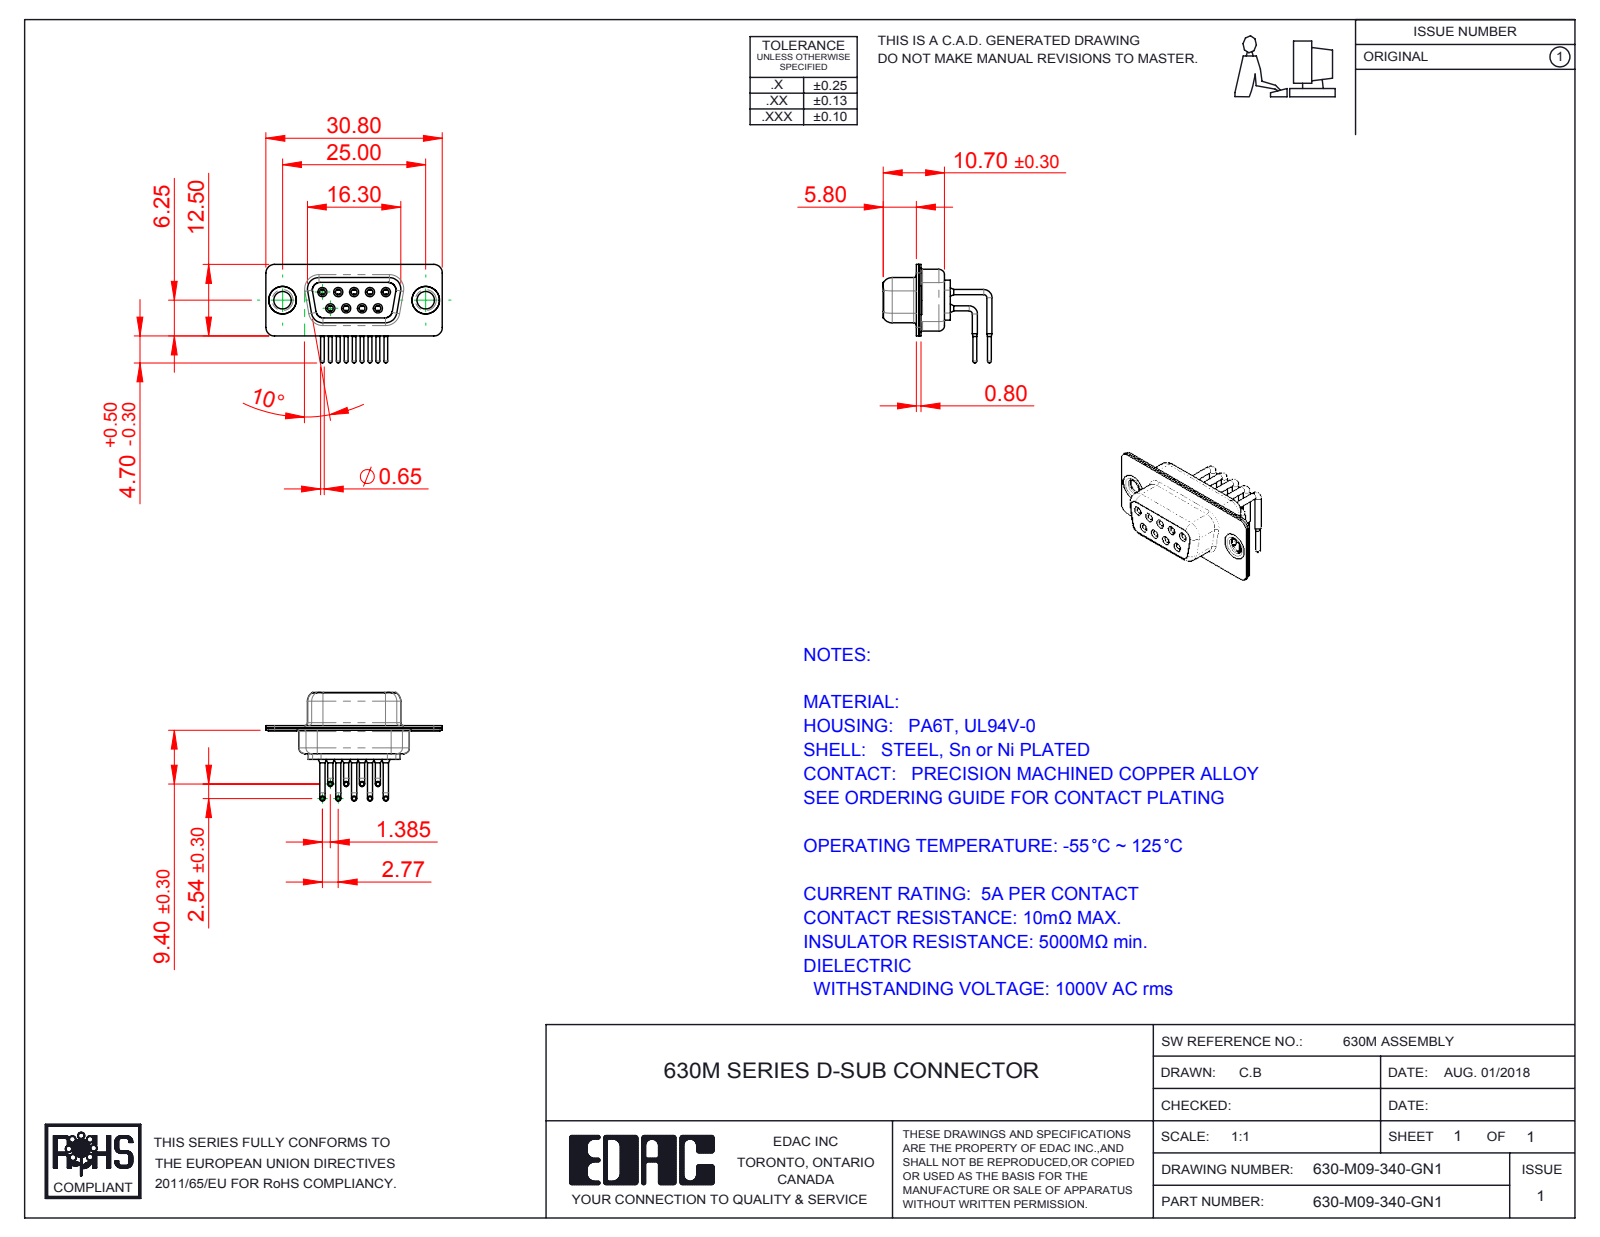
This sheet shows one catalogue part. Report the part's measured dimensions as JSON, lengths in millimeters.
{"part_name": "630M Contact Row 1; 630M Thru Hole Rivet; 630M Shell Front_09 Contacts; 630M Shell Rear_09 Contacts (+3 more)", "step_written_by": "SolidWorks 2016 (CONFIG_CONTROL_DESIGN)", "units": "millimeters", "bodies": {"solids": 14, "faces": 730, "planar": 202, "cylindrical": 328, "other": 200}, "overall_size": [30.8, 18.99, 17.2], "volume_mm3": 1682, "surface_area_mm2": 4490, "round_holes": [[1, 9], [1.1, 9], [1.7, 9], [1.8, 9], [2, 9], [3.05, 2], [4, 2], [4.8, 2]], "round_bosses_or_shafts": [[0.9, 18], [1.6, 9], [1.5, 9], [0.65, 9], [5, 2], [4.9, 2], [3.55, 2]], "partial_cylinders_radius": [[1.5, 16], [2, 12], [1.35, 8], [1.6, 8], [0.25, 4], [0.5, 4], [0.6, 4], [0.65, 4]], "face_to_face_distances": [0.4, 0.8, 1.45, 8.95, 2.3, 6.2, 8.5, 1.9, 0.85, 9.35], "hole_center_spacings": [3.16, 2.77, 5.54, 5.03, 5.04, 8.31, 7.1, 7.48]}
